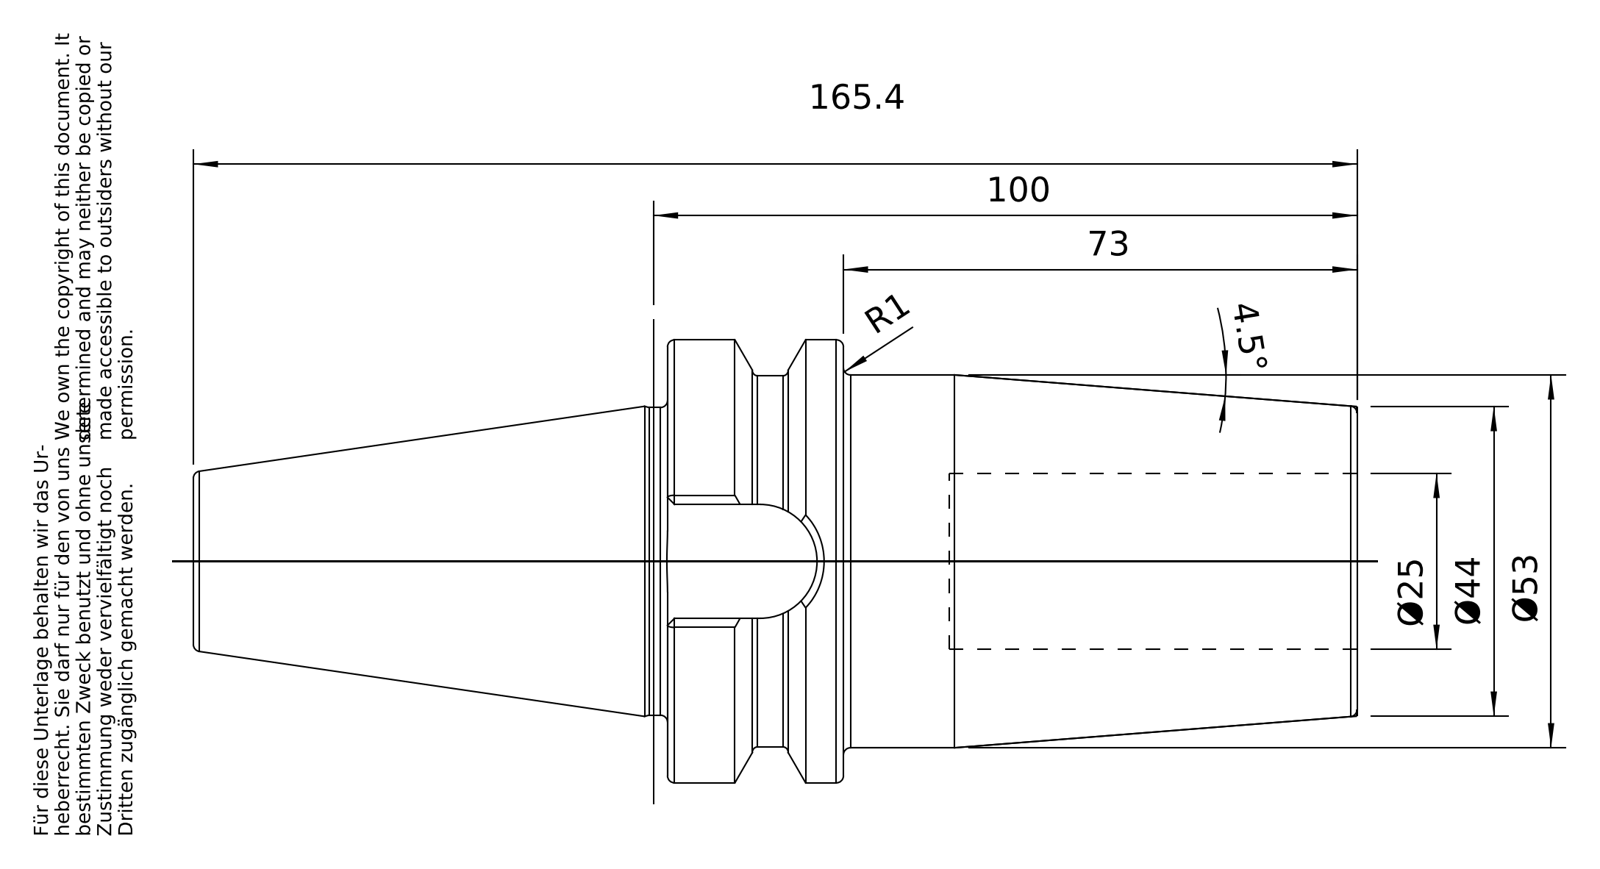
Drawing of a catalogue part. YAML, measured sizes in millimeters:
part_name: "40-640-25"
step_written_by: "PRO/ENGINEER BY PARAMETRIC TECHNOLOGY CORPORATION, 2010430 (CONFIG_CONTROL_DESIGN)"
units: millimeters
bodies: {solids: 1, faces: 96, planar: 26, cylindrical: 22, other: 48}
overall_size: [165.4, 62.98, 62.98]
volume: 238526
surface_area: 36956
round_holes:
  - {diameter: 13.84, count: 1}
  - {diameter: 17.01, count: 1}
  - {diameter: 17.5, count: 1}
  - {diameter: 25, count: 1}
round_bosses_or_shafts:
  - {diameter: 62.98, count: 1}
  - {diameter: 53, count: 1}
  - {diameter: 52.75, count: 1}
  - {diameter: 43.75, count: 1}
  - {diameter: 16.01, count: 1}
partial_cylinders:
  - {radius: 8.1, count: 1}
face_to_face_distances: [98, 25, 73, 40, 15, 58, 44.9, 16.2, 67.4, 92.4]
